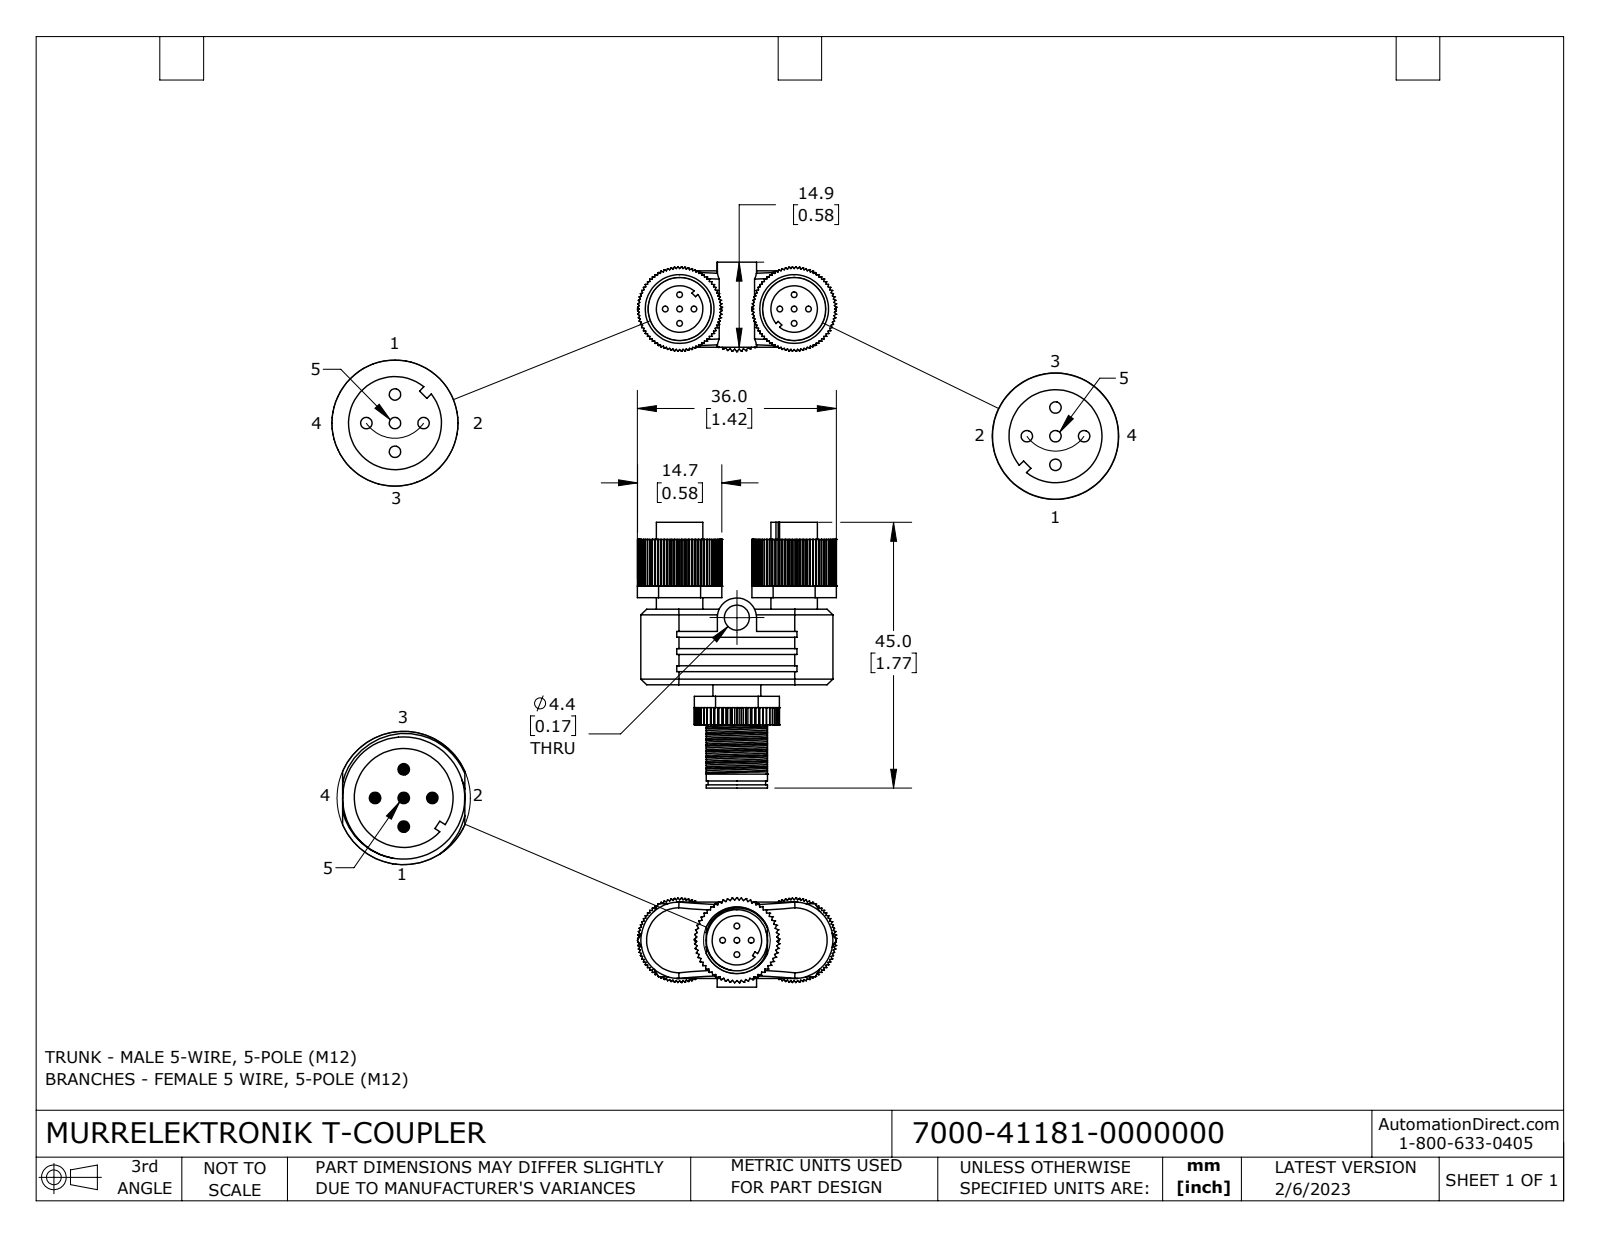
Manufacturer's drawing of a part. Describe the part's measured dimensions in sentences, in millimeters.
The part is named "7000-41181-0000000". Its 3-D file was written by "SolidWorks 2021 (CONFIG_CONTROL_DESIGN)". It is 1 solid with 995 faces: 602 planar, 308 cylindrical and 85 other. Overall it measures 46.39 by 34.73 by 15.62 millimeters. Its volume is 9 860 cubic millimeters and its surface area 6 505 square millimeters. Round holes: 10 of diameter 1, 2 of diameter 11, 1 of diameter 4.37, 1 of diameter 8.63. Round bosses or shafts: 5 of diameter 1, 2 of diameter 8.12, 1 of diameter 10.66, 1 of diameter 10.05, 1 of diameter 8.38. Partial cylindrical surfaces (rounded edges, fillets, slot ends): 2 of radius 6.67, 2 of radius 7.37, 1 of radius 3.42, 1 of radius 5.82, 1 of radius 7.43, 1 of radius 105.6, 1 of radius 105.61. The main face-to-face distances are 9.98, 2, 15.2, 10, 9.99, 5, 27.35, 3, 9.96, 13.2. The hole center spacings are 2.5, 3.54, 20, 5, 10.31, 17.68, 20.16, 22.64.
